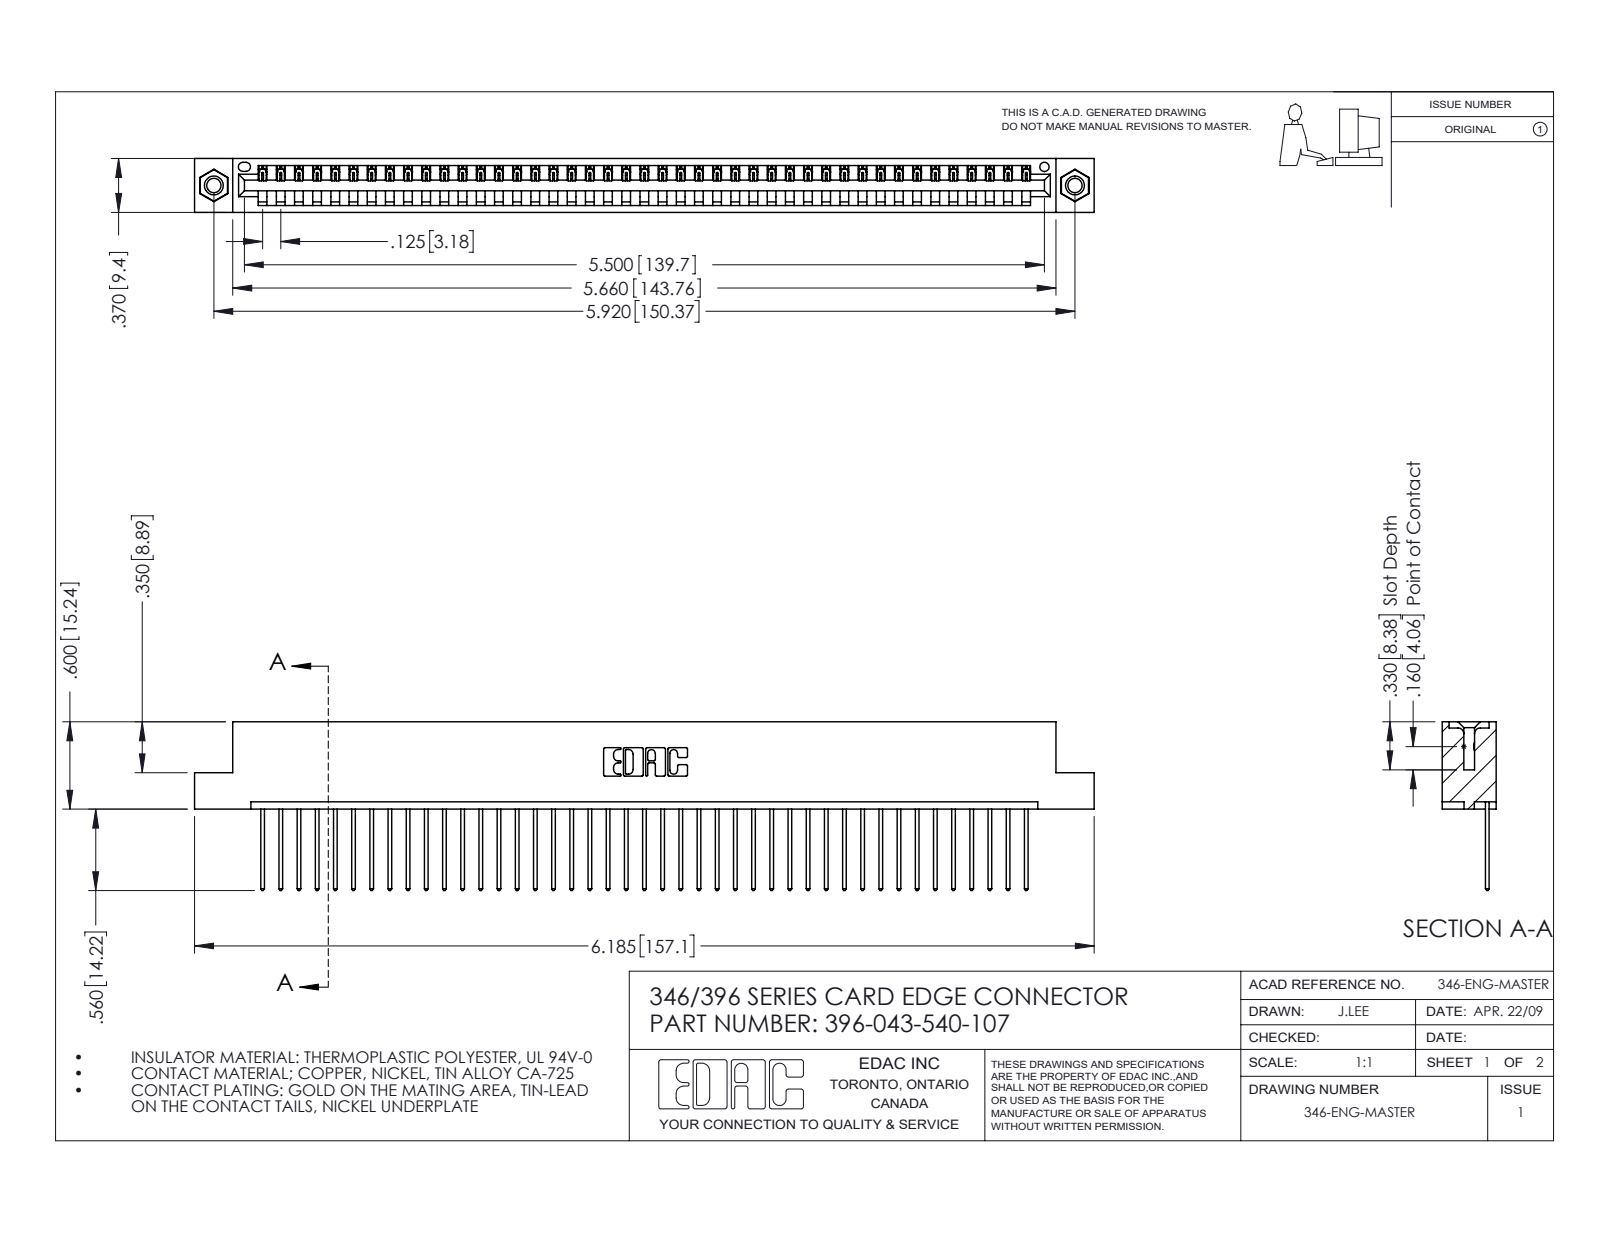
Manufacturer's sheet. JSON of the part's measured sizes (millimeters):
{"part_name": "396-043-540-107; 345-292-001_345-293-140; 346 Part_Flush Mounting Lugs - 0.156 Dia-TI; 345-250-001_345-250-005-103", "step_written_by": "SolidWorks 2016 (CONFIG_CONTROL_DESIGN)", "units": "millimeters", "bodies": {"solids": 46, "faces": 2676, "planar": 1828, "cylindrical": 832, "other": 16}, "overall_size": [157.1, 29.5, 9.4], "volume_mm3": 15100, "surface_area_mm2": 19330, "round_holes": [[2.5, 2], [3.2, 2], [4, 2], [1.6, 1]], "round_bosses_or_shafts": [[3.9, 2]], "partial_cylinders_radius": [[0.2, 86], [0.3, 86], [0.3, 22], [0.2, 6], [0.8, 6], [0.7, 3], [0.8, 2], [1, 2]], "face_to_face_distances": [1.2, 8.2, 9.4, 6.4, 1.8, 7.6, 0.6, 3.8, 5.6, 2.5], "hole_center_spacings": [6.2, 145.1, 150.4]}
